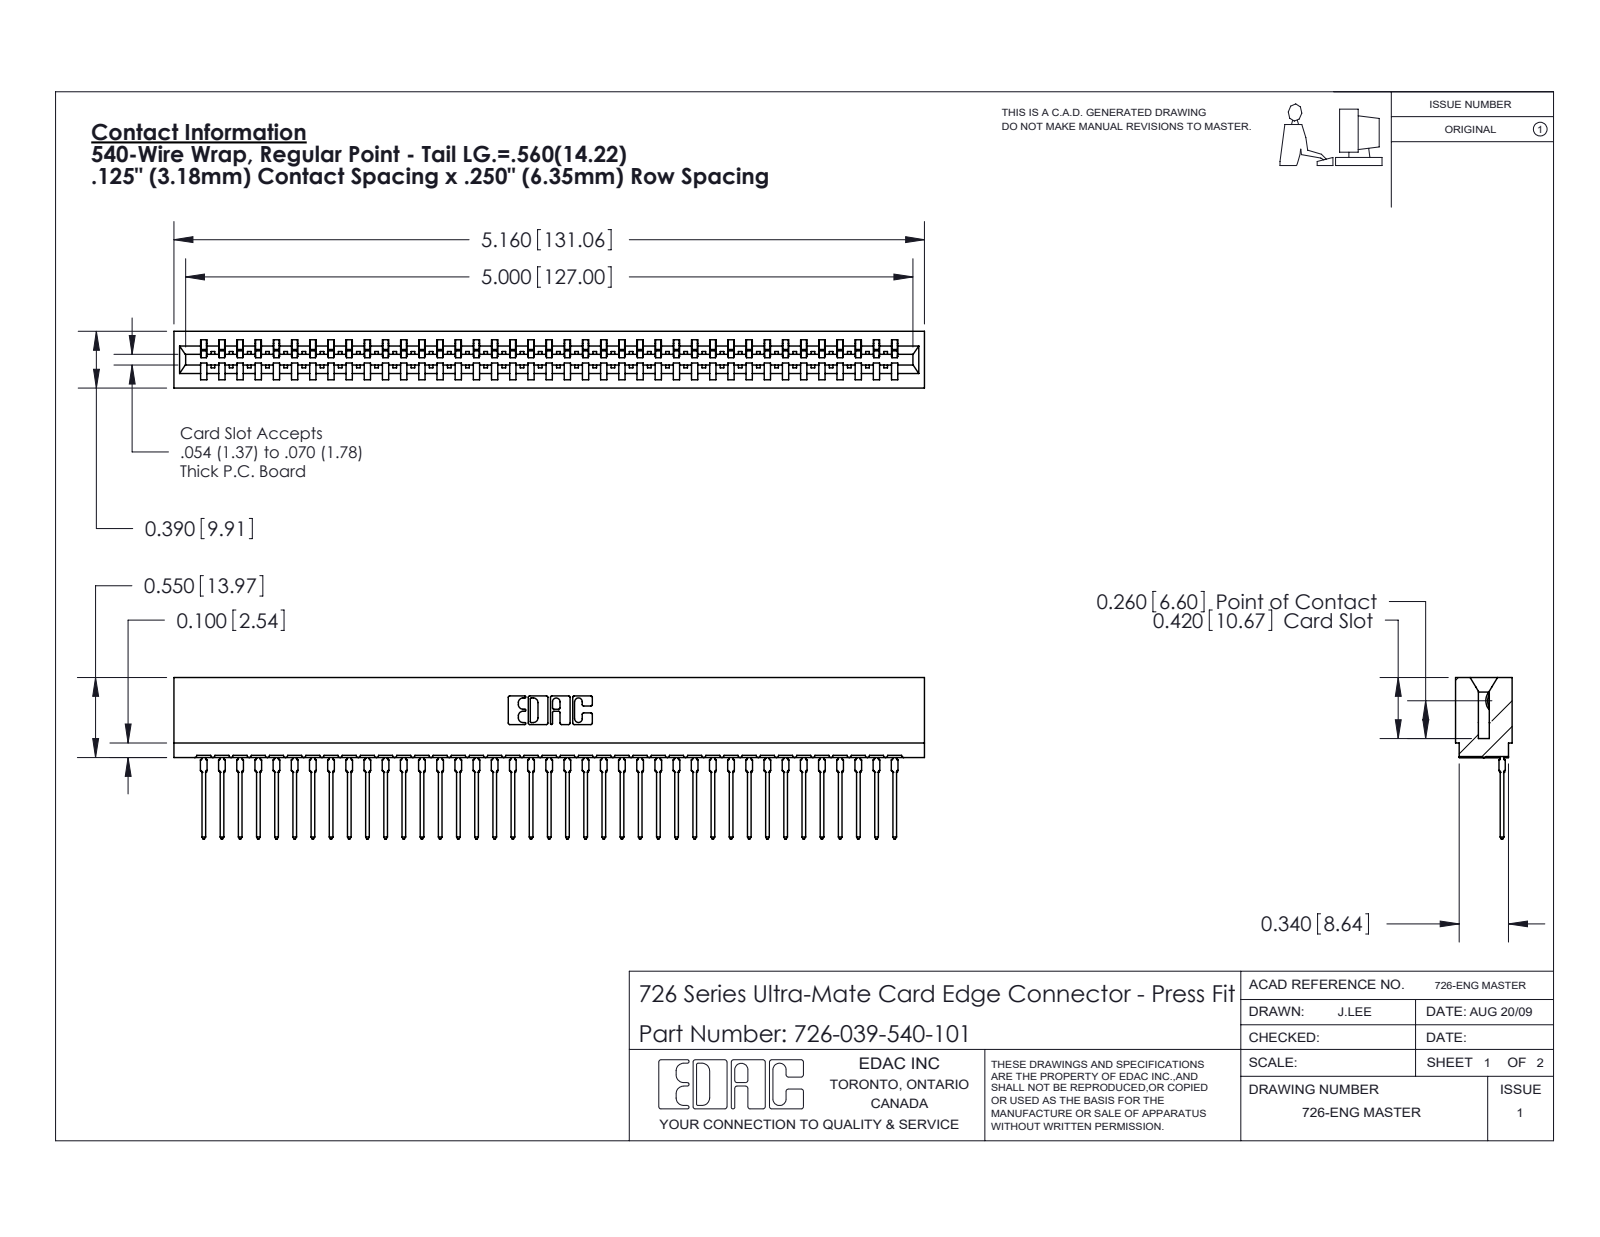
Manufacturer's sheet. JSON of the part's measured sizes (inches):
{"part_name": "726-039-540-101; 726 Part_.515 Slot Depth - 01; 746-292-001_540", "step_written_by": "SolidWorks 2020 (CONFIG_CONTROL_DESIGN)", "units": "inches", "bodies": {"solids": 40, "faces": 4309, "planar": 2512, "cylindrical": 783, "other": 1014}, "overall_size": [5.16, 1.109, 0.39], "volume_in3": 0.721, "surface_area_in2": 28.6, "partial_cylinders_radius": [[0.021, 78], [0.015, 40], [0.01, 22], [0.007, 6], [0.031, 6], [0.005, 4], [0.011, 4], [0.026, 3]], "face_to_face_distances": [0.057, 0.333, 0.39, 0.025, 0.307, 0.25, 0.083, 0.275, 0.365, 0.032]}
